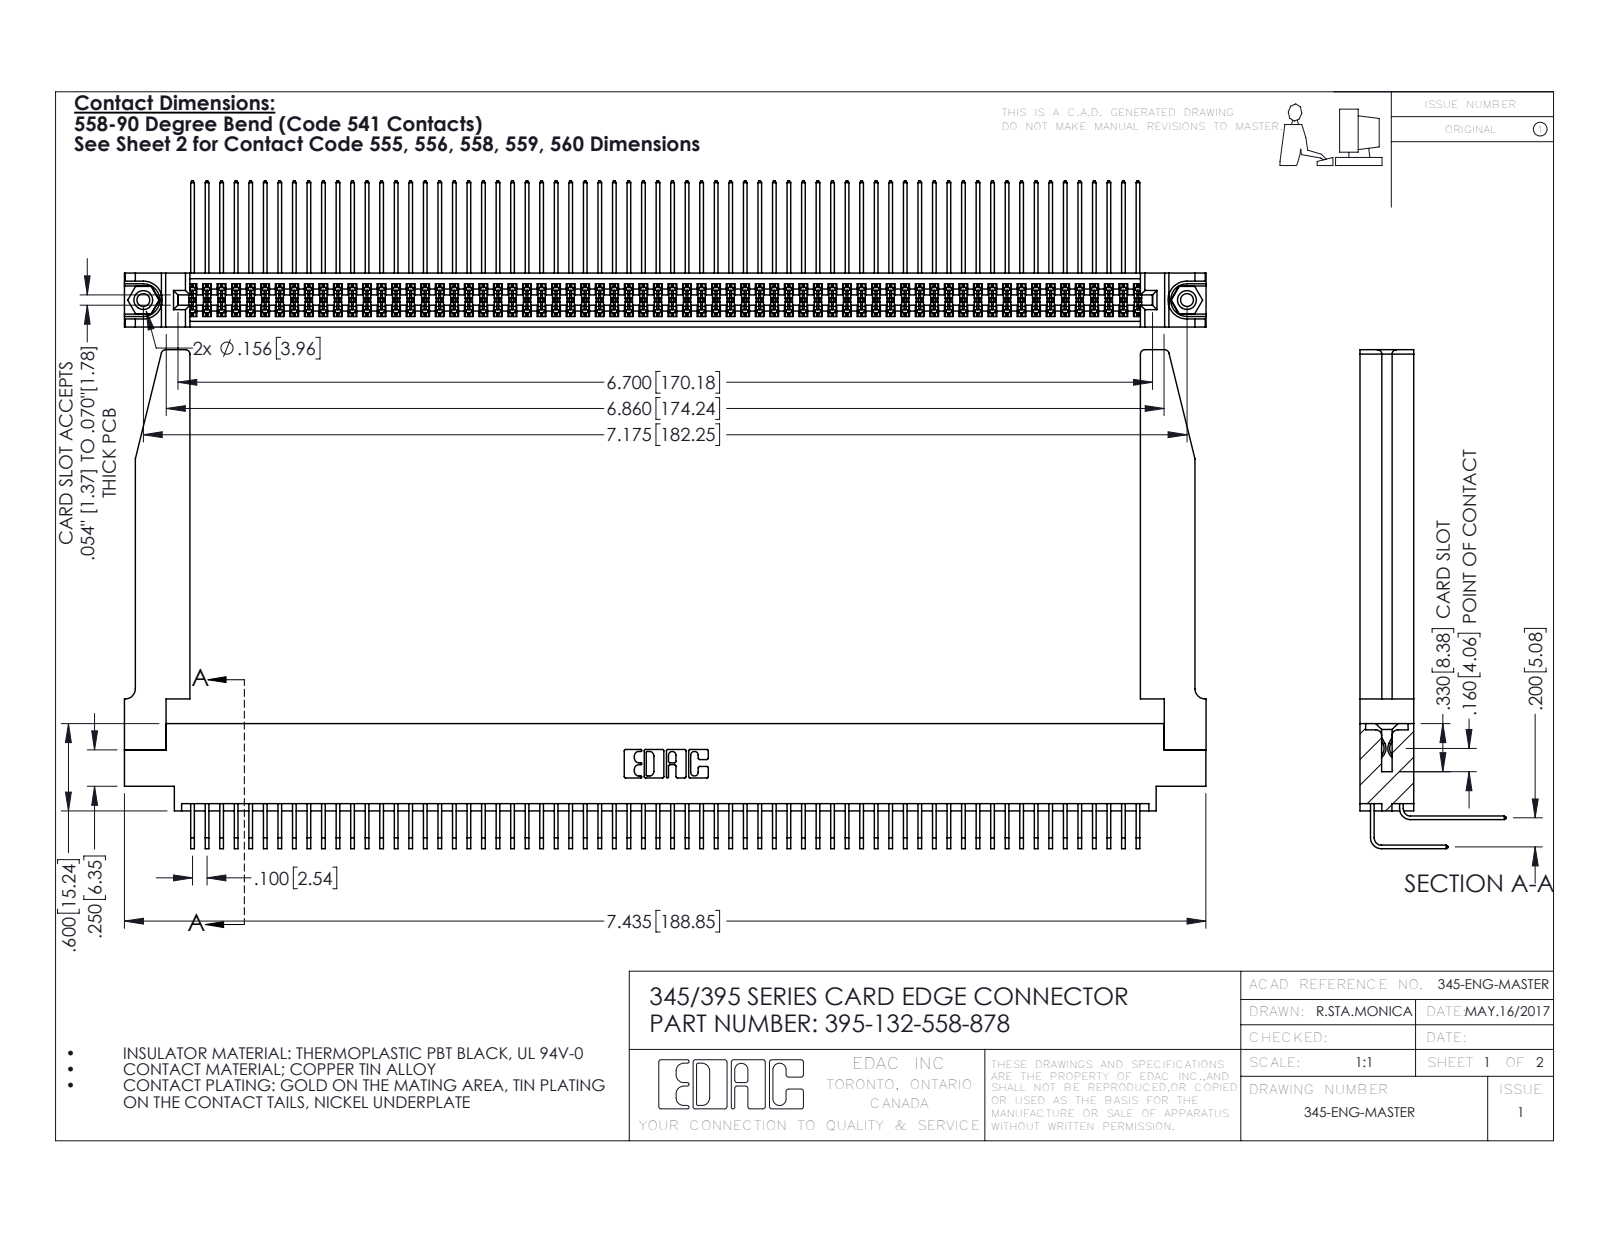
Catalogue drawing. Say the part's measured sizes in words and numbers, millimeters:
The part is named "345-250-001_345-250-001-102; 395-132-558-878; 345-220-078_345-220-078; 345-292-001_558 Tail - 2 (+2 more)". Its 3-D file was written by "SolidWorks 2016 (CONFIG_CONTROL_DESIGN)". It is 137 solids with 7228 faces: 4846 planar, 2330 cylindrical and 52 other. Overall it measures 188.9 by 87.1 by 25.5 millimeters. Its volume is 26 990 cubic millimeters and its surface area 39 430 square millimeters. Round holes: 2 of diameter 2.3, 2 of diameter 3.2, 2 of diameter 4, 1 of diameter 1.6. Round bosses or shafts: 2 of diameter 3.9. Partial cylindrical surfaces (rounded edges, fillets, slot ends): 198 of radius 0.2, 22 of radius 0.3, 8 of radius 0.8, 6 of radius 0.2, 6 of radius 0.8, 3 of radius 0.7, 2 of radius 0.4, 2 of radius 0.5. The main face-to-face distances are 1.8, 7.6, 9.4, 5.1, 2.5, 6.9, 0.6, 5.7, 4.4, 0.6. The hole center spacings are 6.9, 176.3, 182.2.
